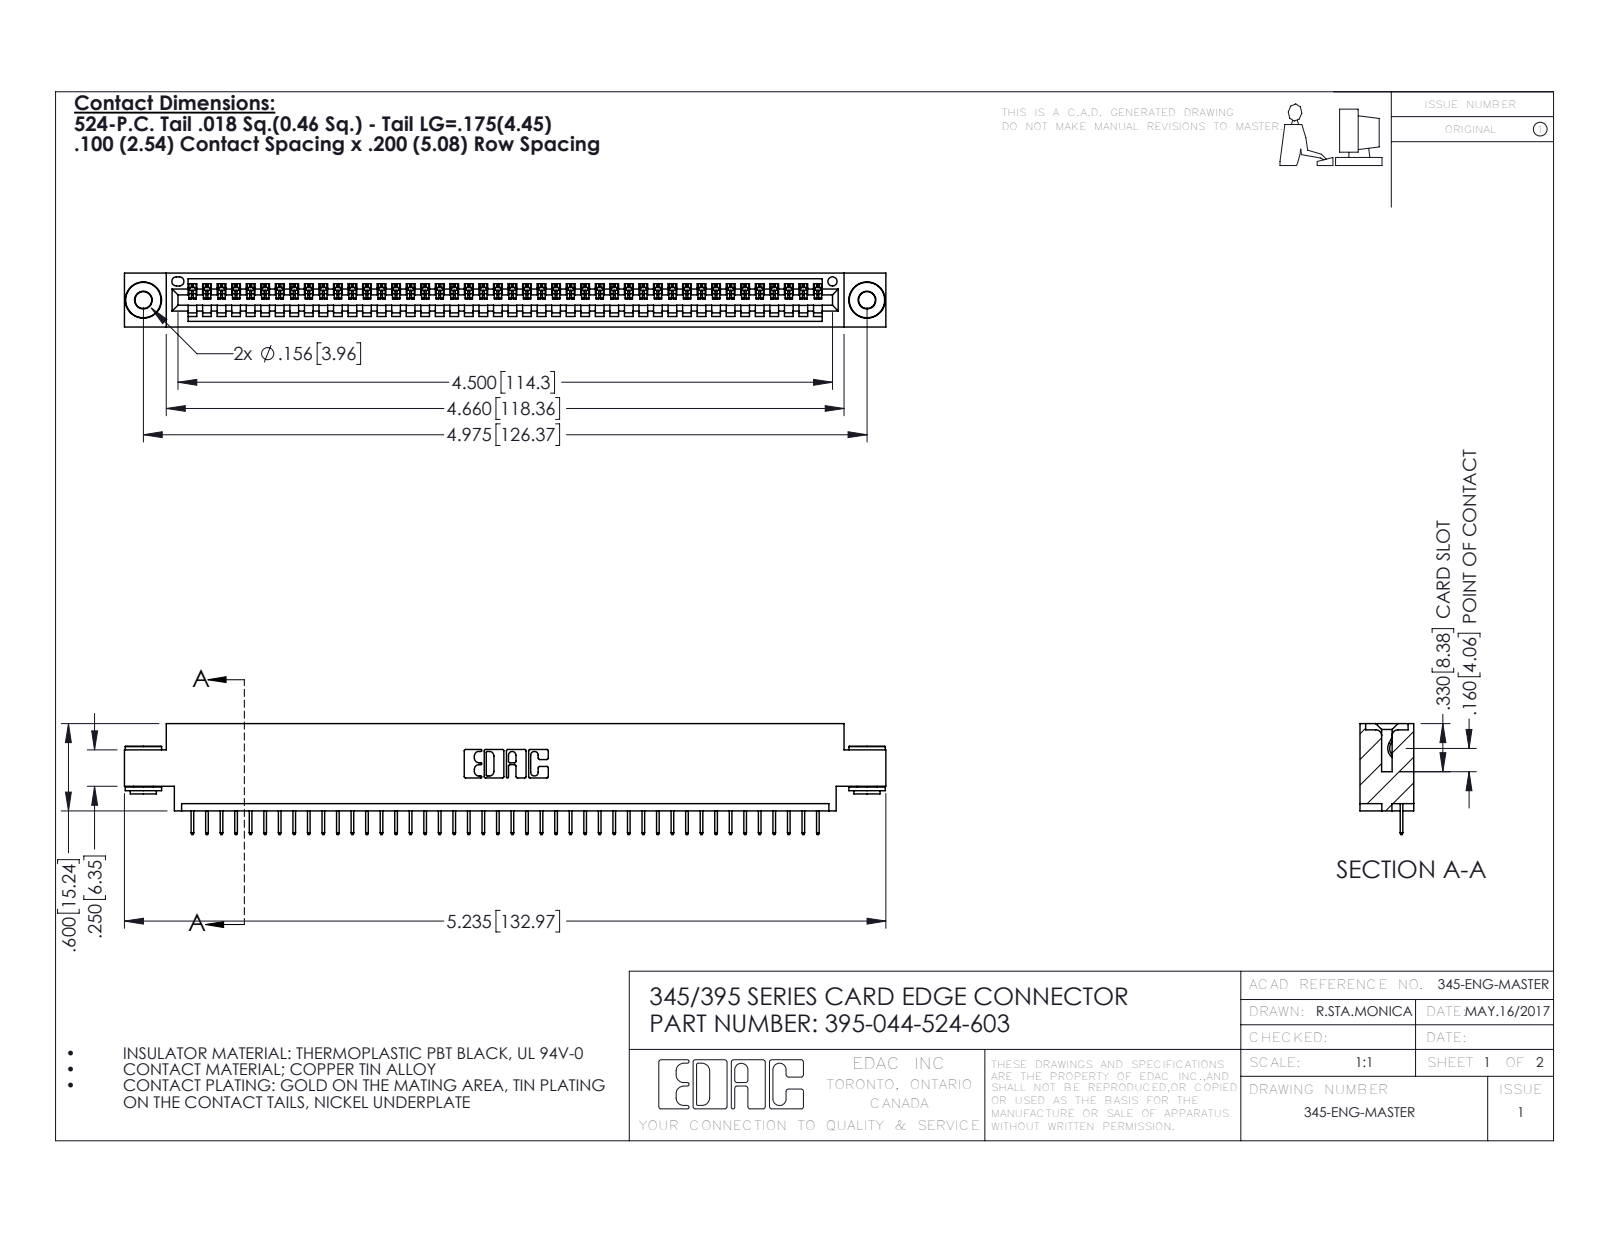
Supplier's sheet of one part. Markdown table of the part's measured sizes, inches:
| quantity | value |
| --- | --- |
| part name | 345 Part_0.170 Offset - 0.156 Dia-TH; 345-250-002_345-250-002-102; 345-292-001_345-293-124; 395-044-524-603 |
| STEP written by | SolidWorks 2016 (CONFIG_CONTROL_DESIGN) |
| units | inches |
| bodies | 47 solids, 2896 faces (2118 planar, 770 cylindrical, 8 other) |
| overall size | 5.235 × 0.762 × 0.37 |
| volume | 0.755 in³ |
| surface area | 25.21 in² |
| round holes (diameter × count) | 0.116 × 2, 0.156 × 2, 0.064 × 1 |
| round bosses / shafts (diameter × count) | 0.25 × 2, 0.18 × 2, 0.136 × 2 |
| partial cylindrical surfaces (radius × count) | 0.006 × 88, 0.01 × 22, 0.007 × 6, 0.031 × 6, 0.026 × 3, 0.031 × 2, 0.04 × 2, 0.014 × 1 |
| main face-to-face distances | 0.072, 0.298, 0.37, 0.2, 0.098, 0.272, 0.025, 0.225, 0.175, 0.072 |
| hole center spacings | 0.27, 4.739, 4.975 |
